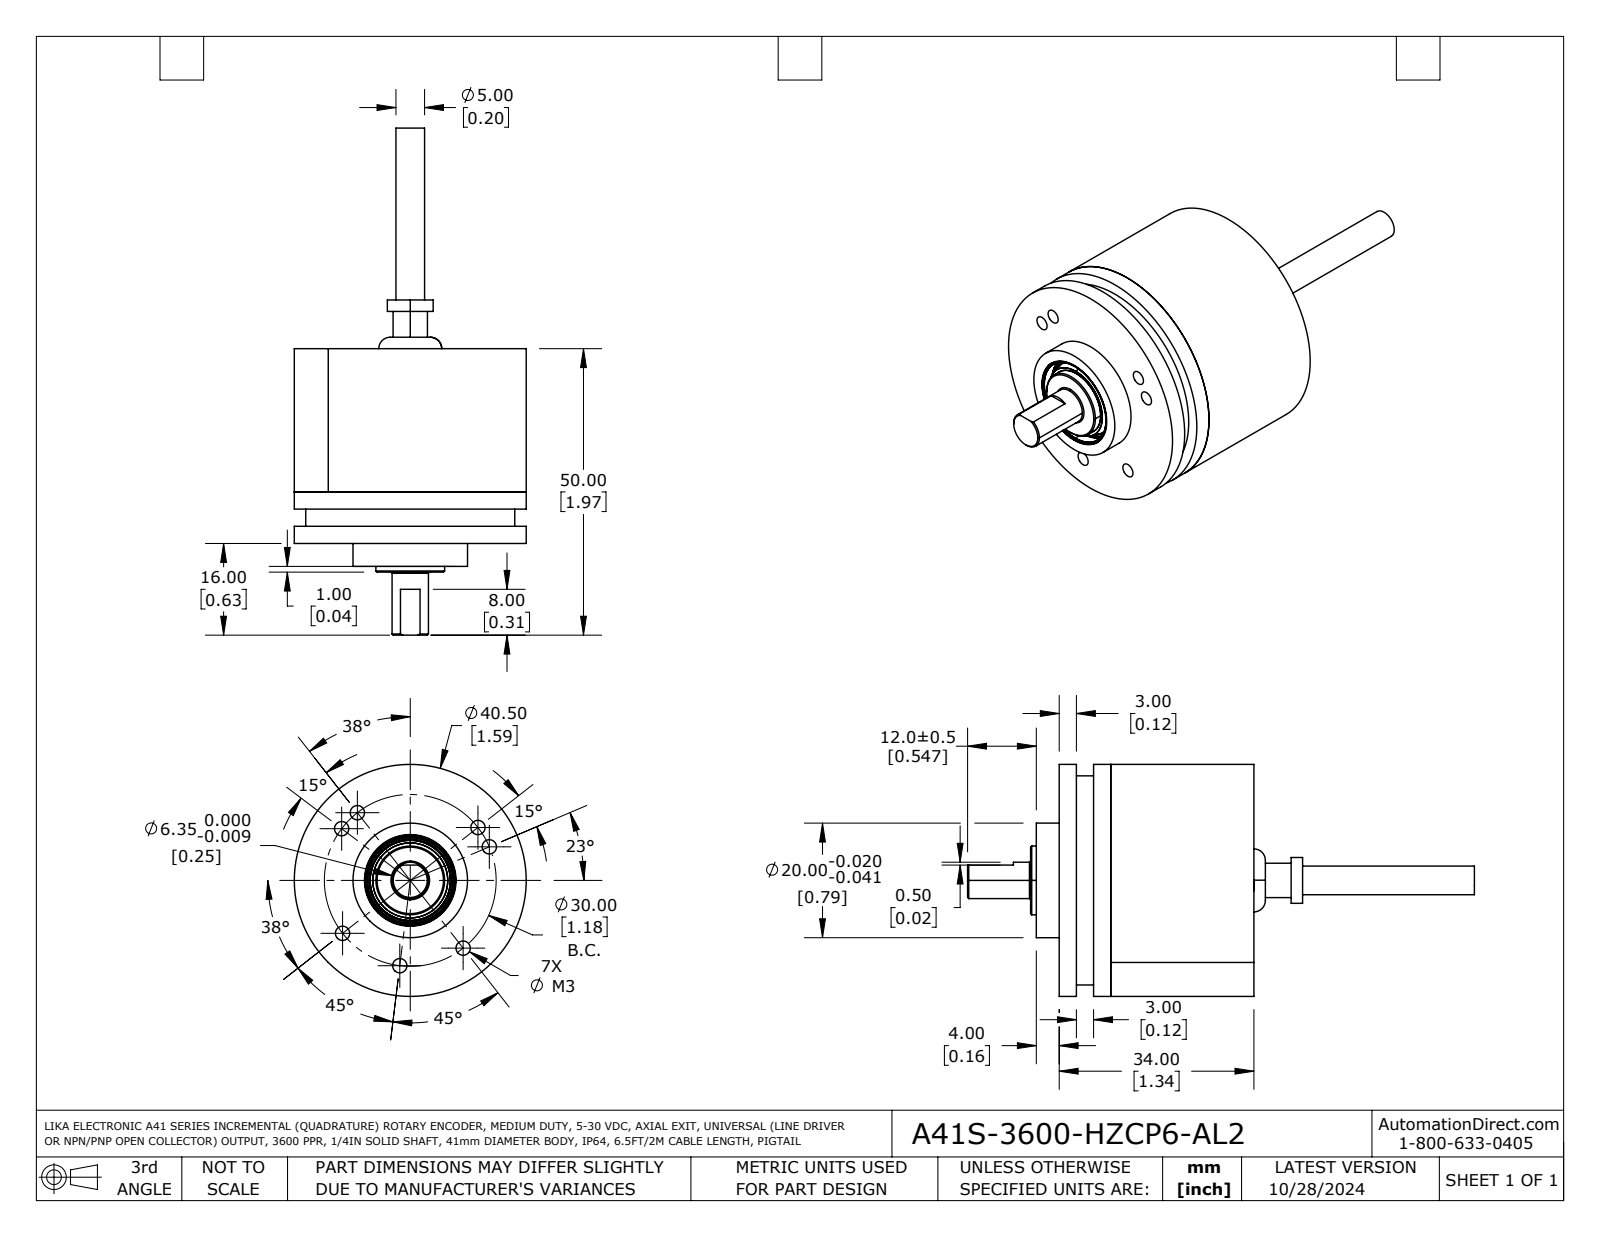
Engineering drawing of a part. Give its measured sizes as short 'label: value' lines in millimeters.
name: A41S-3600-HZCP6-AL2
written by: SolidWorks 2021 (AUTOMOTIVE_DESIGN)
unit: mm
bodies: 11 solids, 422 faces (76 planar, 145 cylindrical, 201 other)
size: 88.5 × 40.5 × 40.5
volume: 19 250 mm³; area: 18 250 mm²
holes: 7× ⌀1.6, 7× ⌀2.5, 3× ⌀4, 2× ⌀2.2, 1× ⌀4.3, 1× ⌀7.5, 1× ⌀13, 1× ⌀15.3, 1× ⌀15.5, 1× ⌀16, 1× ⌀38.5
bosses: 2× ⌀2, 1× ⌀40.5, 1× ⌀38, 1× ⌀37, 1× ⌀36.5, 1× ⌀20, 1× ⌀12, 1× ⌀8
rounds: 14× R1, 6× R0.2, 2× R0.2
face distances: 3, 34, 11, 23, 31, 2, 22, 25, 20, 1
hole spacings: 15, 17, 21.2, 2.8, 3, 21.3, 24, 31.9
